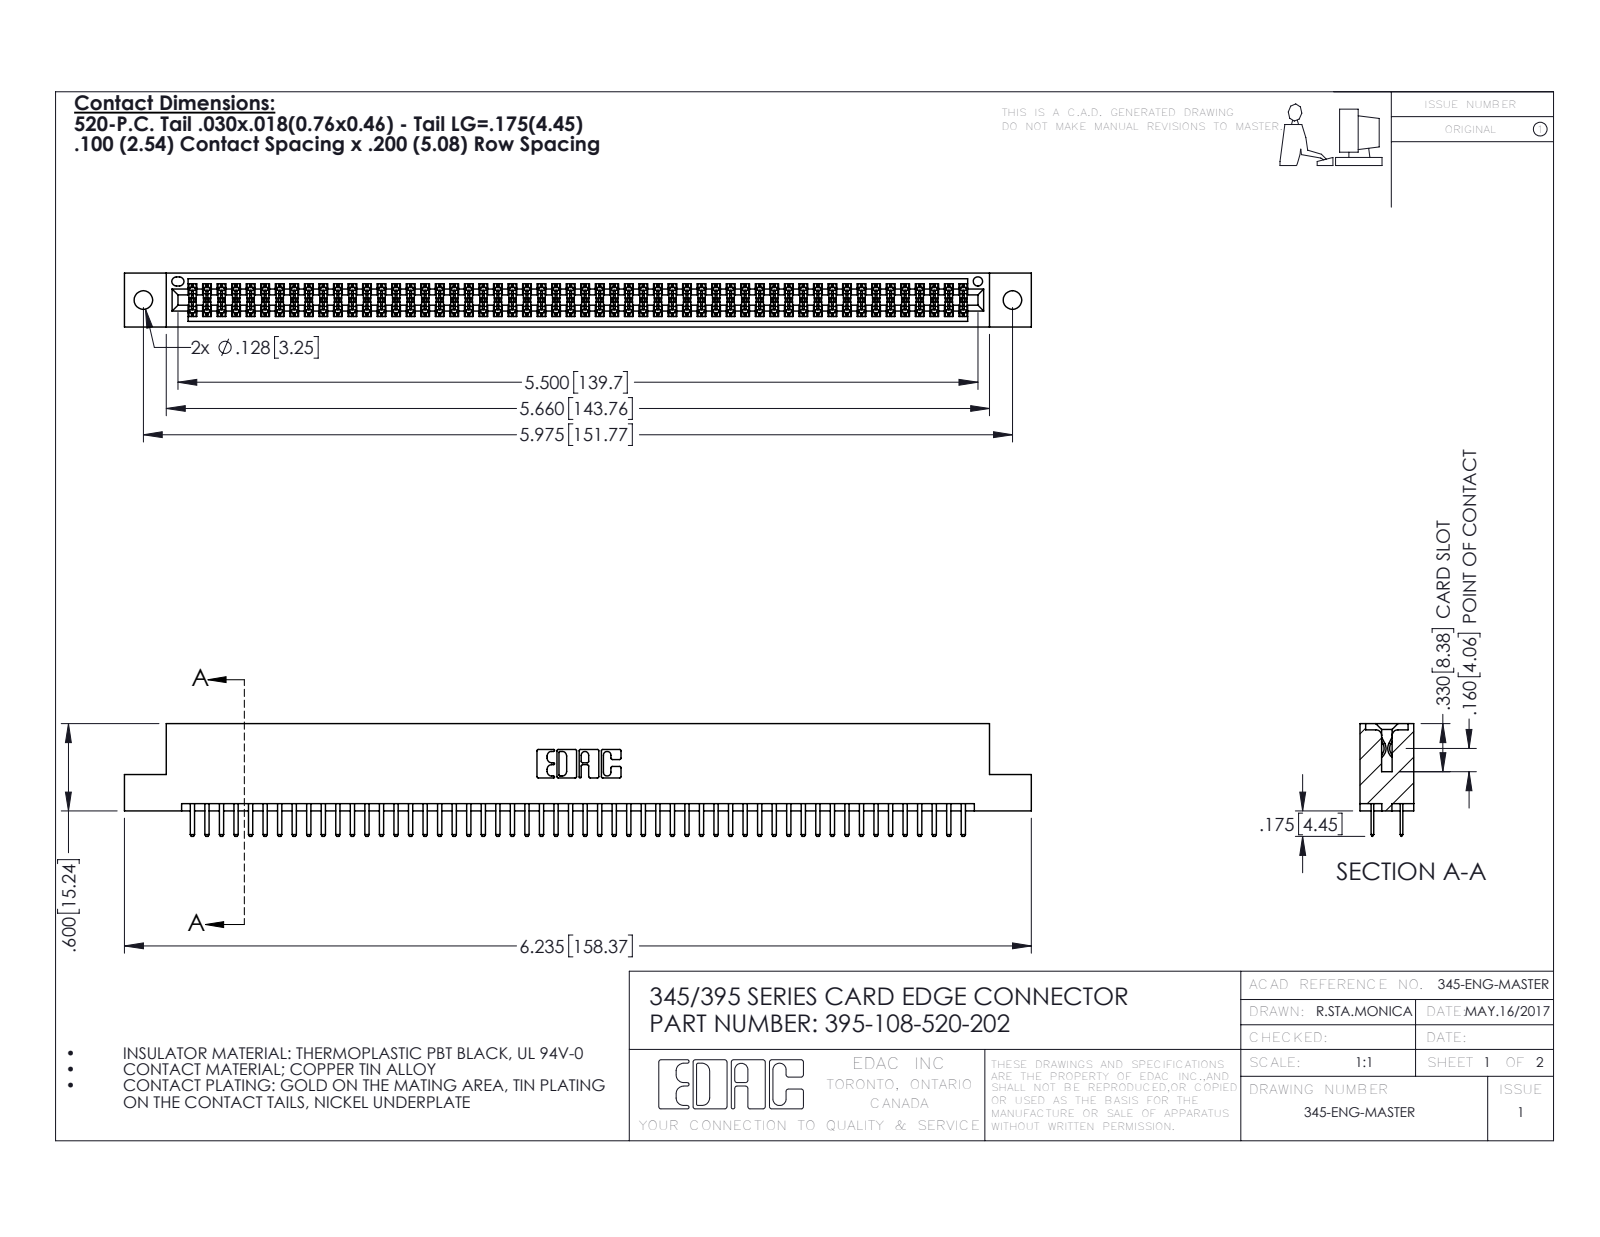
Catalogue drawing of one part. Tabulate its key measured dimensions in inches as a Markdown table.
| quantity | value |
| --- | --- |
| part name | 345-292-001_345-293-120; 345 Part_Flush Mounting Lugs - 0.128 Dia; 395-108-520-202 |
| STEP written by | SolidWorks 2016 (CONFIG_CONTROL_DESIGN) |
| units | inches |
| bodies | 109 solids, 5958 faces (3860 planar, 2098 cylindrical, 0 other) |
| overall size | 6.235 × 0.775 × 0.37 |
| volume | 0.94 in³ |
| surface area | 35.09 in² |
| round holes (diameter × count) | 0.128 × 2, 0.064 × 1 |
| partial cylindrical surfaces (radius × count) | 0.006 × 162, 0.01 × 112, 0.01 × 22, 0.007 × 6, 0.031 × 6, 0.026 × 3, 0.014 × 2, 0.019 × 2 |
| main face-to-face distances | 0.298, 0.072, 0.2, 0.37, 0.098, 0.272, 0.025, 0.225, 0.022, 0.072 |
| hole center spacings | 0.27, 5.739, 5.975 |
